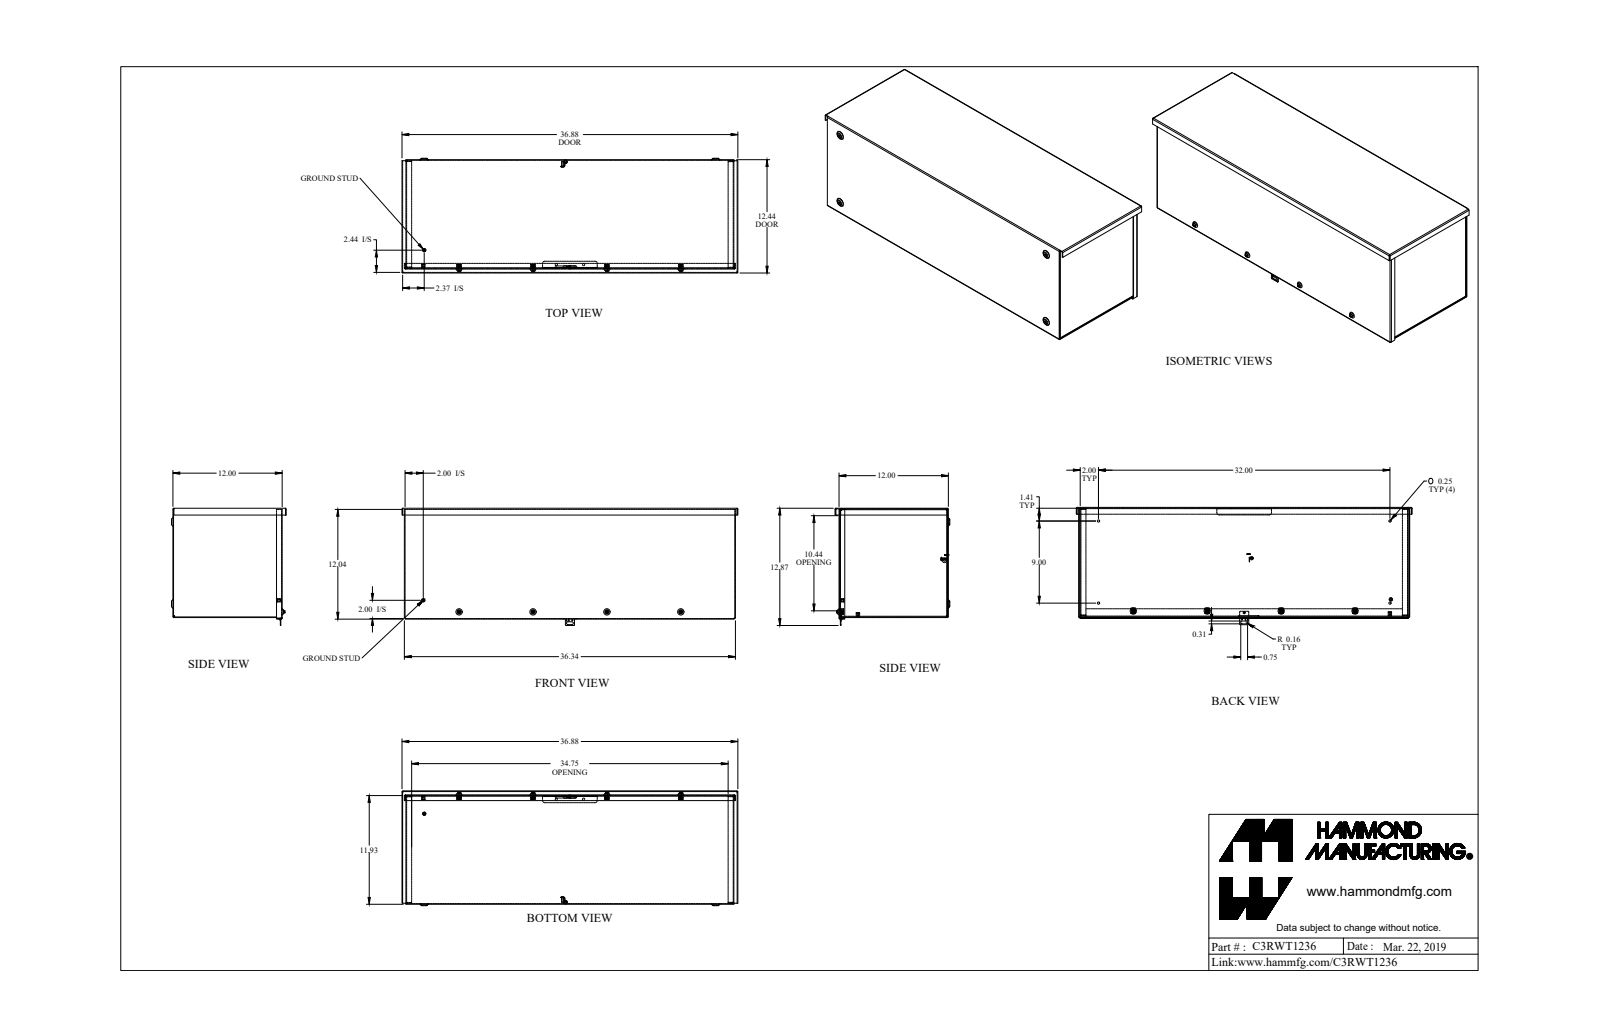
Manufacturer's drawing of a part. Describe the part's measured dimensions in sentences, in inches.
The part is named "C3RWT1236_Default". Its 3-D file was written by "SolidWorks 2019 (CONFIG_CONTROL_DESIGN)". It is 25 solids with 885 faces: 486 planar, 275 cylindrical and 124 other. Overall it measures 36.875 by 12.871 by 12.594 inches. Its volume is 157.9 cubic inches and its surface area 4 422 square inches. Round holes: 6 of diameter 0.156, 6 of diameter 0.25, 4 of diameter 0.214, 4 of diameter 0.23, 2 of diameter 0.203, 1 of diameter 0.125, 1 of diameter 0.137, 1 of diameter 0.2, 1 of diameter 0.215. Round bosses or shafts: 5 of diameter 0.19, 4 of diameter 0.148, 2 of diameter 0.375, 1 of diameter 0.5, 1 of diameter 0.367, 1 of diameter 0.21, 1 of diameter 0.152, 1 of diameter 0.125. Partial cylindrical surfaces (rounded edges, fillets, slot ends): 18 of radius 0.036, 18 of radius 0.108, 16 of radius 0.08, 16 of radius 0.108, 12 of radius 0.125, 8 of radius 0.022, 6 of radius 0.25, 4 of radius 0.016. The main face-to-face distances are 0.072, 11.928, 11.856, 12, 35.928, 36, 35.856, 0.172, 0.144, 11.784. The hole center spacings are 8.115, 16.23, 3.927, 4.061, 7.792, 8.115, 10.484, 11.875.
